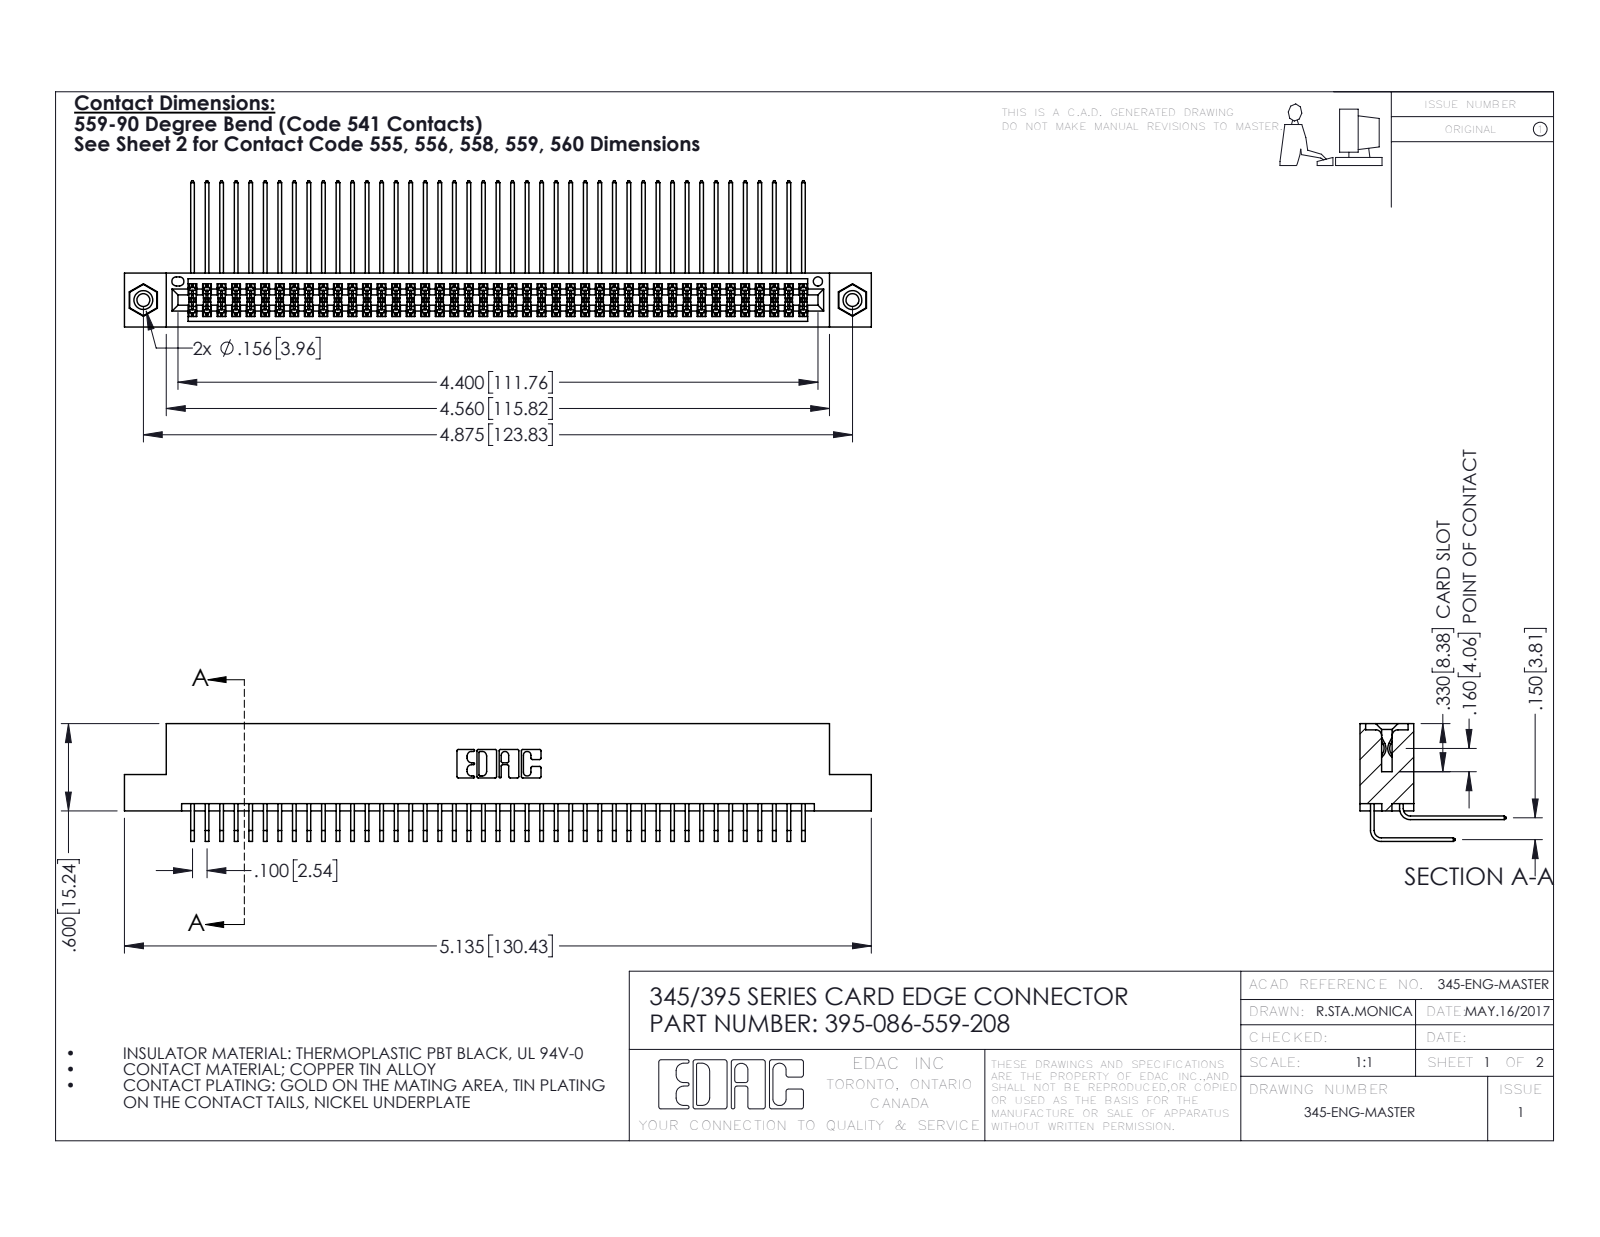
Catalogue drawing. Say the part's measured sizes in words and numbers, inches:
The part is named "345-292-001_559 Tail - 2; 395-086-559-208; 345-292-001_558 559 Tail - 1; 345 Part_Flush Mounting Lugs - 0.156 Dia-TI (+1 more)". Its 3-D file was written by "SolidWorks 2016 (CONFIG_CONTROL_DESIGN)". It is 89 solids with 4658 faces: 3122 planar, 1520 cylindrical and 16 other. Overall it measures 5.135 by 1.005 by 0.809 inches. Its volume is 0.804 cubic inches and its surface area 33.84 square inches. Round holes: 2 of diameter 0.089, 2 of diameter 0.125, 2 of diameter 0.156, 1 of diameter 0.064. Round bosses or shafts: 2 of diameter 0.155. Partial cylindrical surfaces (rounded edges, fillets, slot ends): 130 of radius 0.006, 22 of radius 0.01, 6 of radius 0.007, 6 of radius 0.031, 3 of radius 0.026, 2 of radius 0.014, 2 of radius 0.019, 2 of radius 0.022. The main face-to-face distances are 0.072, 0.298, 0.2, 0.37, 0.098, 0.272, 0.025, 0.225, 0.175, 0.15. The hole center spacings are 0.27, 4.639, 4.875.
